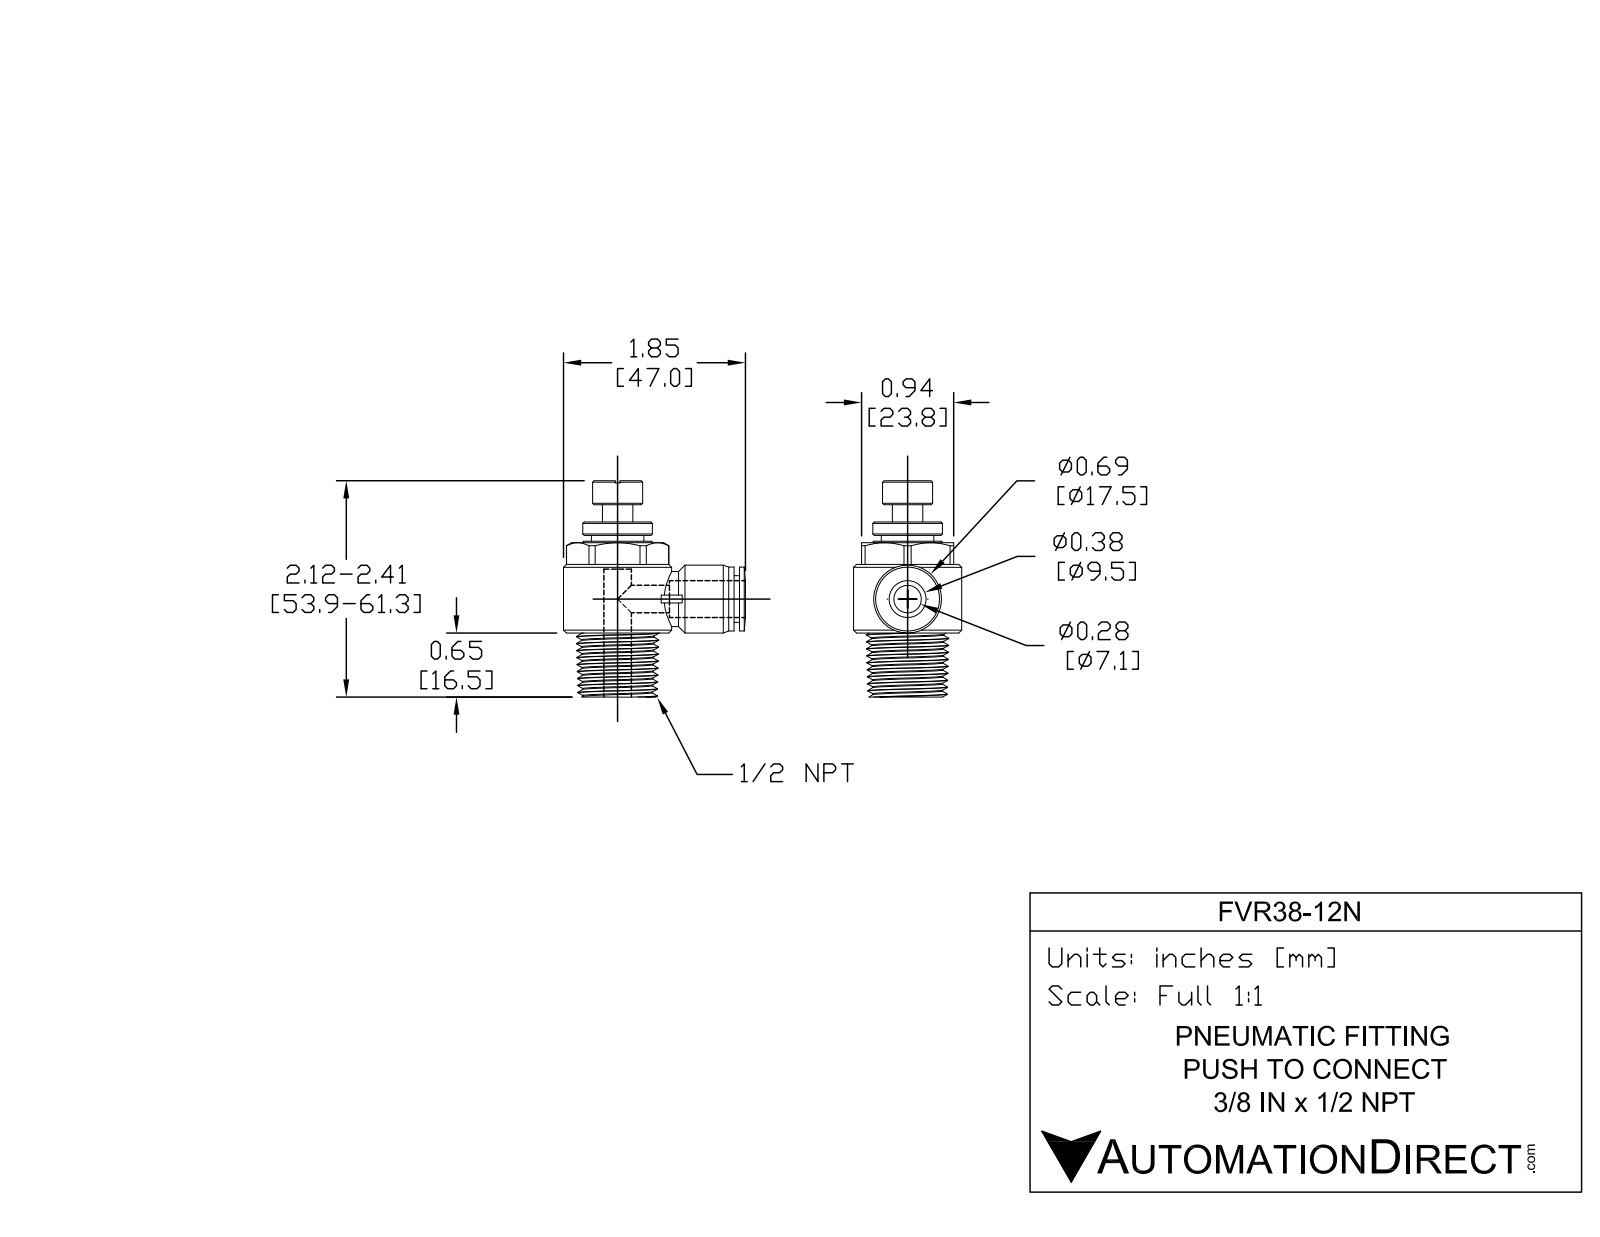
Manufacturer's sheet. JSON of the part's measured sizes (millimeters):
{"part_name": "FVR38-12N", "step_written_by": "SolidWorks 2015 (AUTOMOTIVE_DESIGN)", "units": "millimeters", "bodies": {"solids": 1, "faces": 576, "planar": 259, "cylindrical": 149, "other": 168}, "overall_size": [61.3, 47.2, 28], "volume_mm3": 23450, "surface_area_mm2": 8239, "round_holes": [[7, 2], [9.8, 1]], "round_bosses_or_shafts": [[14, 2], [28, 1], [24, 1], [21.9, 1], [18.1, 1], [17.5, 1], [17, 1], [16.8, 1]], "partial_cylinders_radius": [[6.5, 1], [9, 1], [13, 1]], "face_to_face_distances": [41.2, 17.7, 23.5, 46.5, 28.8, 5.3, 24, 1.2, 25.3, 43]}
